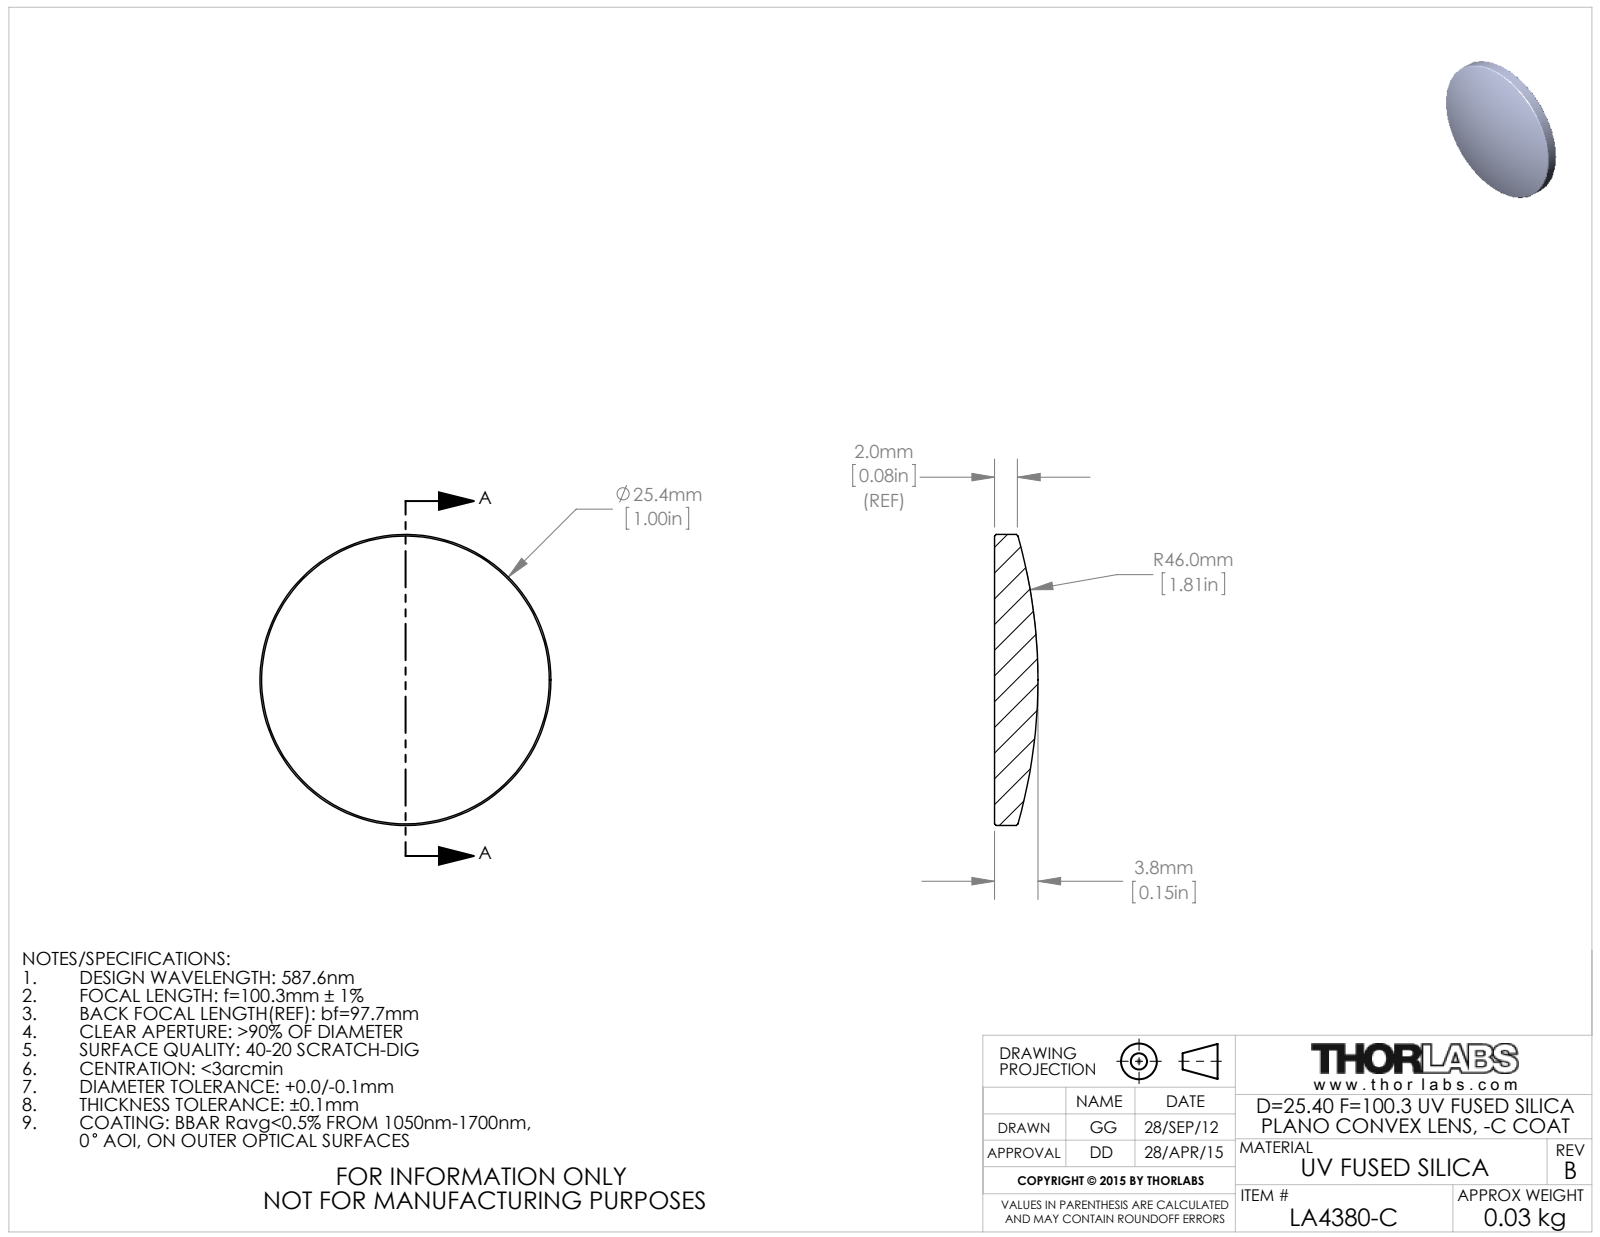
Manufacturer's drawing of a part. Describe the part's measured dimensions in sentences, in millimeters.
The part is named "24983-E0W". Its 3-D file was written by "SolidWorks 2014 (CONFIG_CONTROL_DESIGN)". It is 1 solid with 9 faces: 1 planar, 2 cylindrical and 6 other. Overall it measures 25.4 by 25.4 by 3.79 millimeters. Its volume is 1 468 cubic millimeters and its surface area 1 173 square millimeters. Round bosses or shafts: 1 of diameter 25.4.
